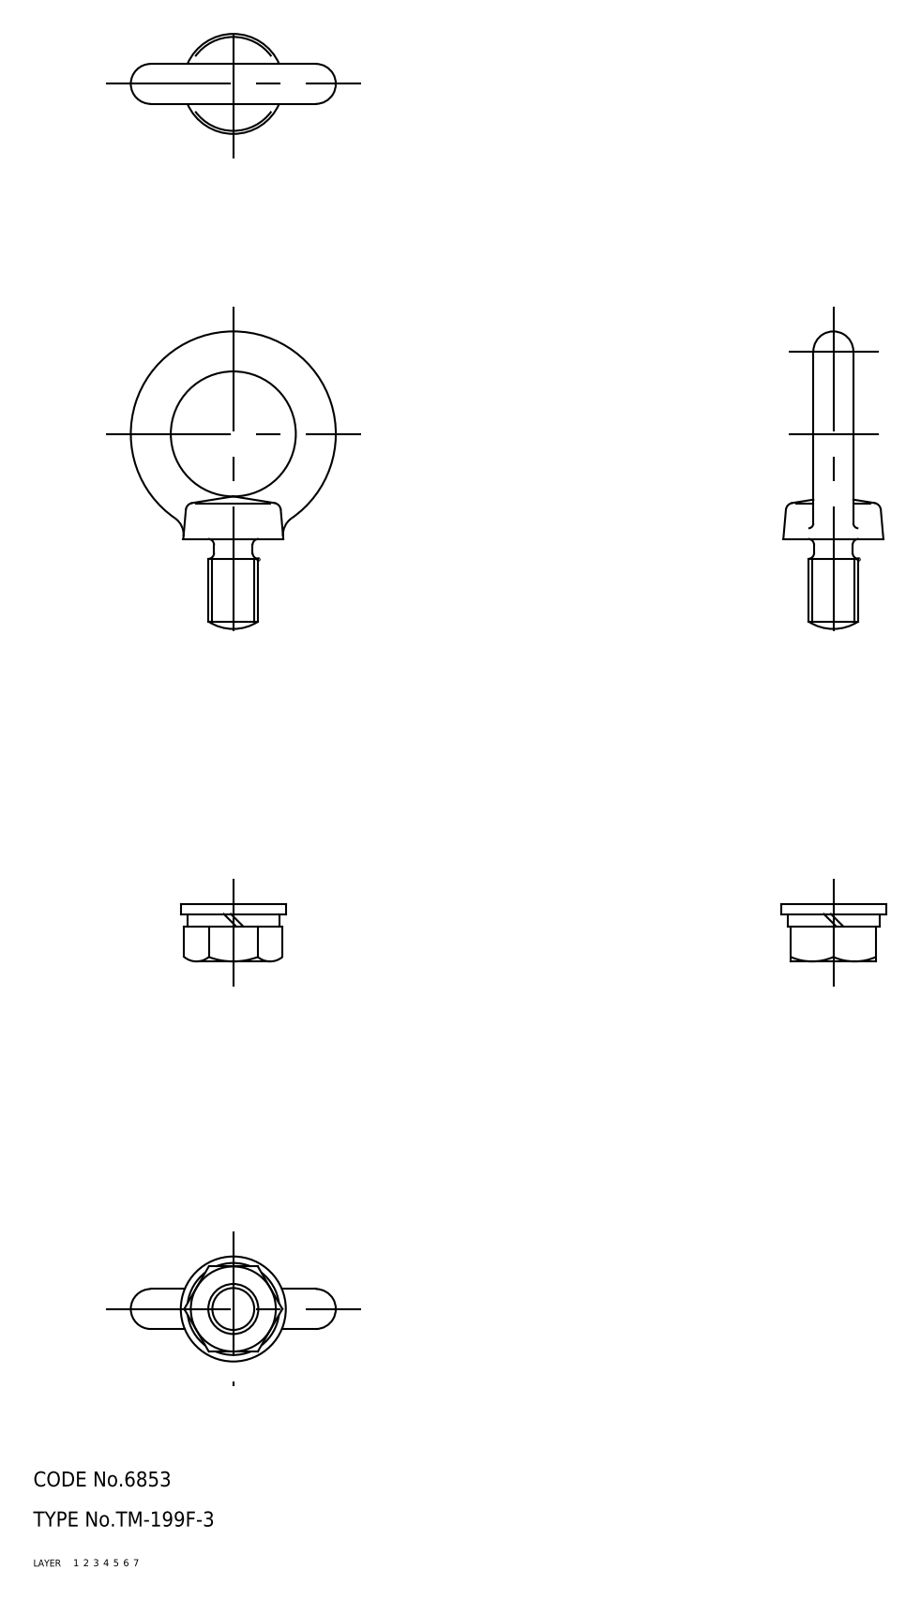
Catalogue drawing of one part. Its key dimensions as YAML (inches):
part_name: "TM_199F_3"
step_written_by: "SolidWorks 2003240 (AUTOMOTIVE_DESIGN)"
units: inches
bodies: {solids: 4, faces: 52, planar: 13, cylindrical: 12, other: 27}
overall_size: [2.343, 1.614, 0.827]
volume: 0.623
surface_area: 9.176
round_holes:
  - {diameter: 0.394, count: 1}
round_bosses_or_shafts:
  - {diameter: 0.827, count: 1}
  - {diameter: 0.724, count: 1}
face_to_face_distances: [0.079, 0.098, 0.177, 0.669, 0.276, 0.374, 0.453]
